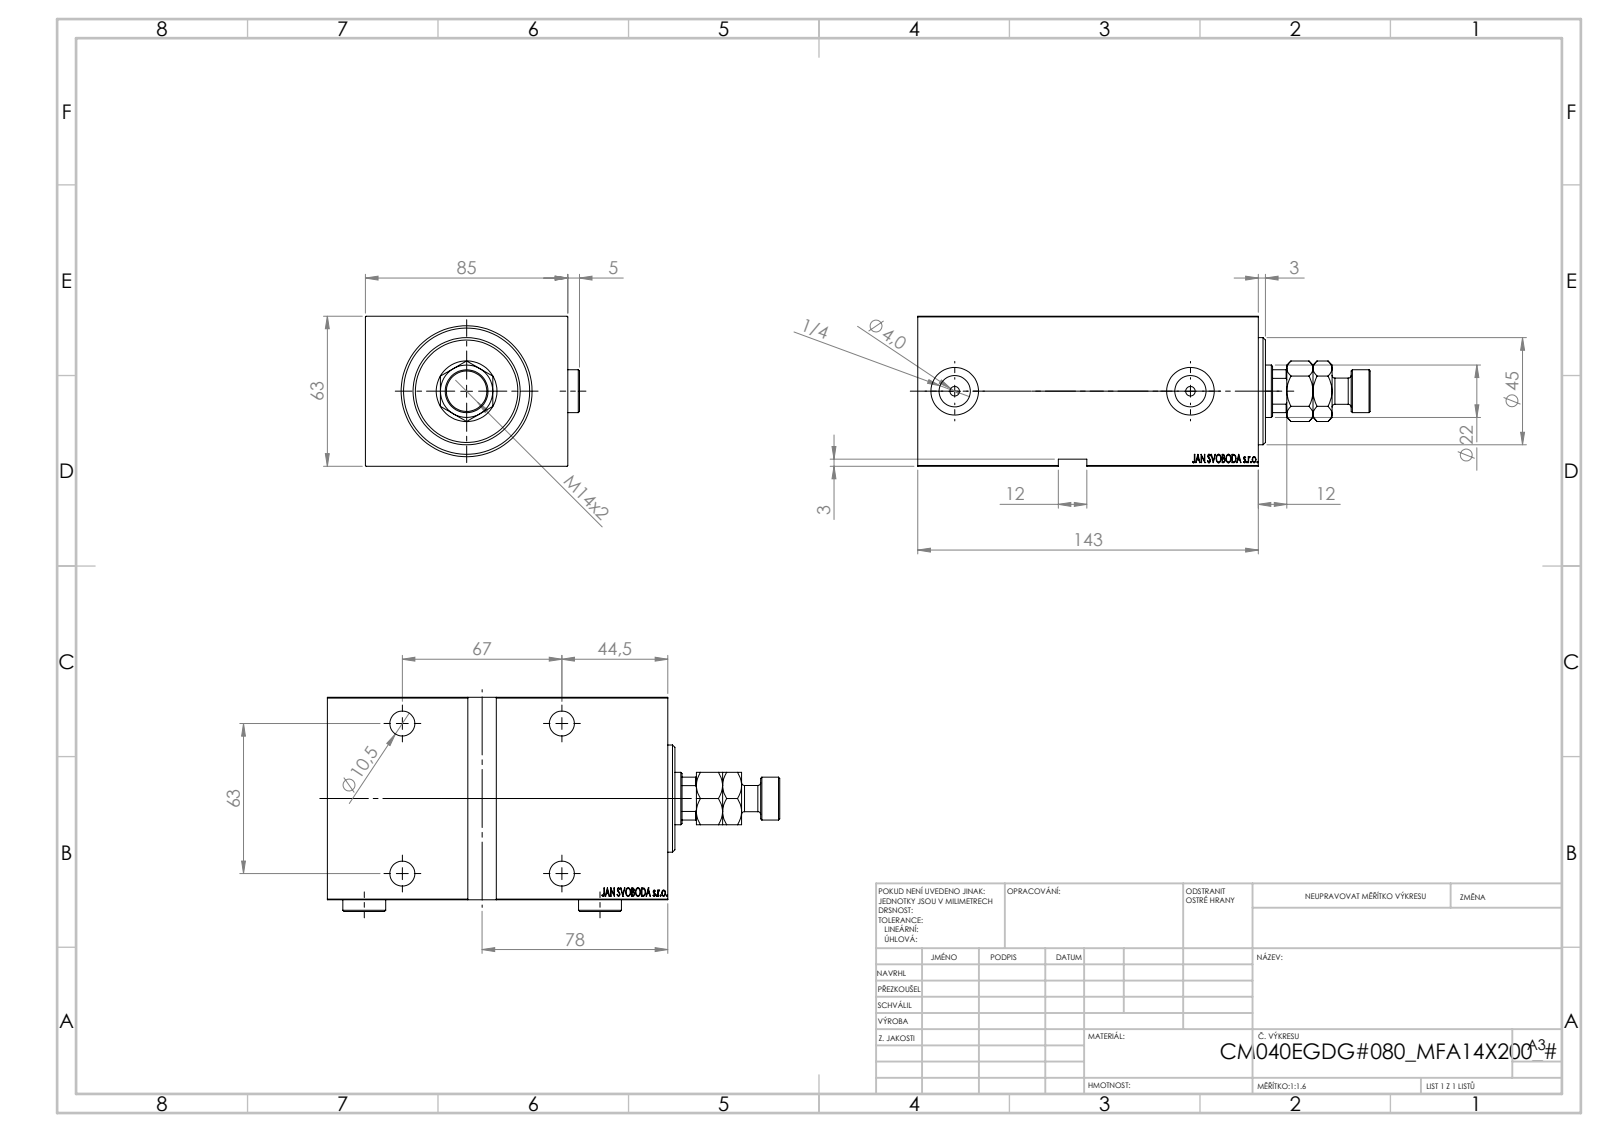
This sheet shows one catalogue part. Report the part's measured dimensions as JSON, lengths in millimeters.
{"part_name": "V450CM_VC_B; MFA; V450CM_E_VCP; Zatka_OIL_PORT (+1 more)", "step_written_by": "SolidWorks 2019 (CONFIG_CONTROL_DESIGN)", "units": "millimeters", "bodies": {"solids": 6, "faces": 964, "planar": 462, "cylindrical": 72, "other": 430}, "overall_size": [190, 89.9, 63], "volume_mm3": 677858, "surface_area_mm2": 109482, "round_holes": [[10.5, 4], [16.5, 4], [4, 2], [13.16, 2], [20, 2], [12.5, 1], [22, 1], [25.5, 1], [40, 1], [53, 1]], "round_bosses_or_shafts": [[18, 3], [45, 1], [42, 1], [11, 1]], "partial_cylinders_radius": [[10.5, 1]], "face_to_face_distances": [63, 85, 143, 12, 131, 5, 3, 126, 138, 8], "hole_center_spacings": [63, 67, 91.97, 99]}
